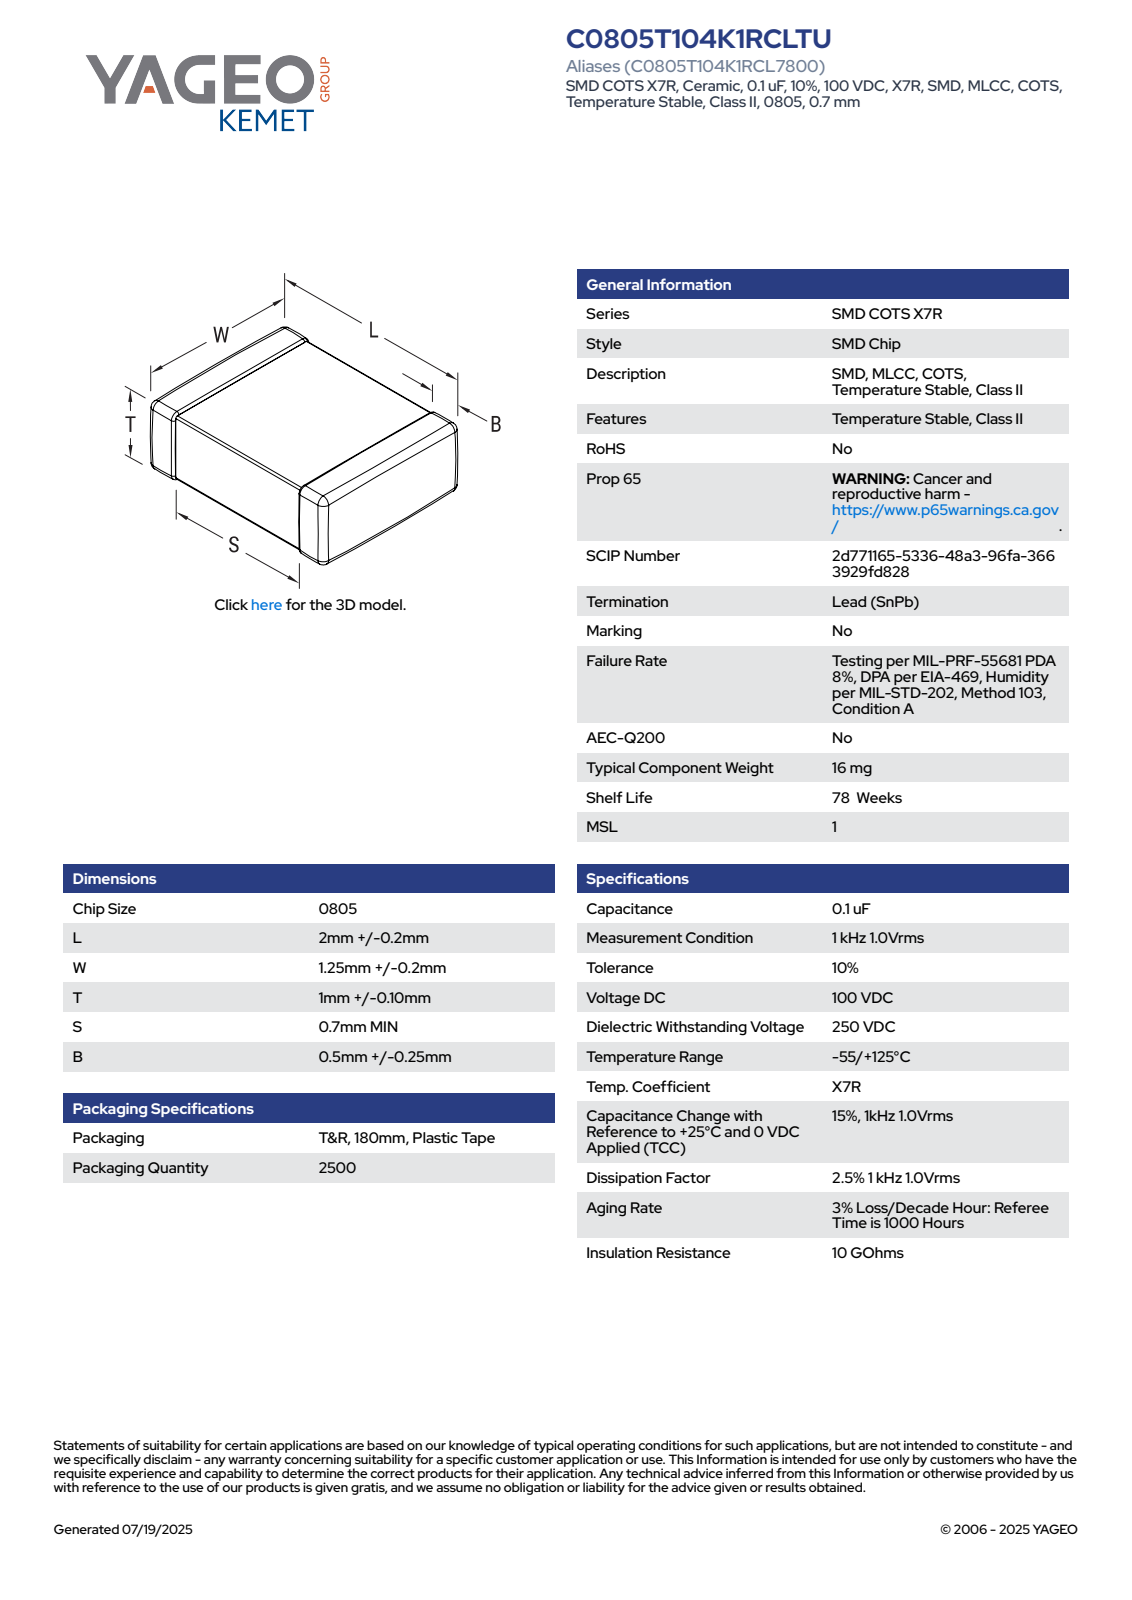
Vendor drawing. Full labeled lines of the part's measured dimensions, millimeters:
Part name (STEP PRODUCT): CCSM_STD_0805_L2.2W1.45T1.1B0.75
STEP written by: SolidWorks 2014 (AUTOMOTIVE_DESIGN)
Units: millimetres
Bodies: 4 solids, 125 faces (71 planar, 38 cylindrical, 16 other)
Overall size (bounding box): 2.2 × 1.45 × 1.1
Volume: 3 mm³ · Surface area: 14 mm²
Main face-to-face distances: 1.07, 1.1, 2.2, 1.45, 1.42, 1.04, 1.39, 0.7, 0.72, 0.73
